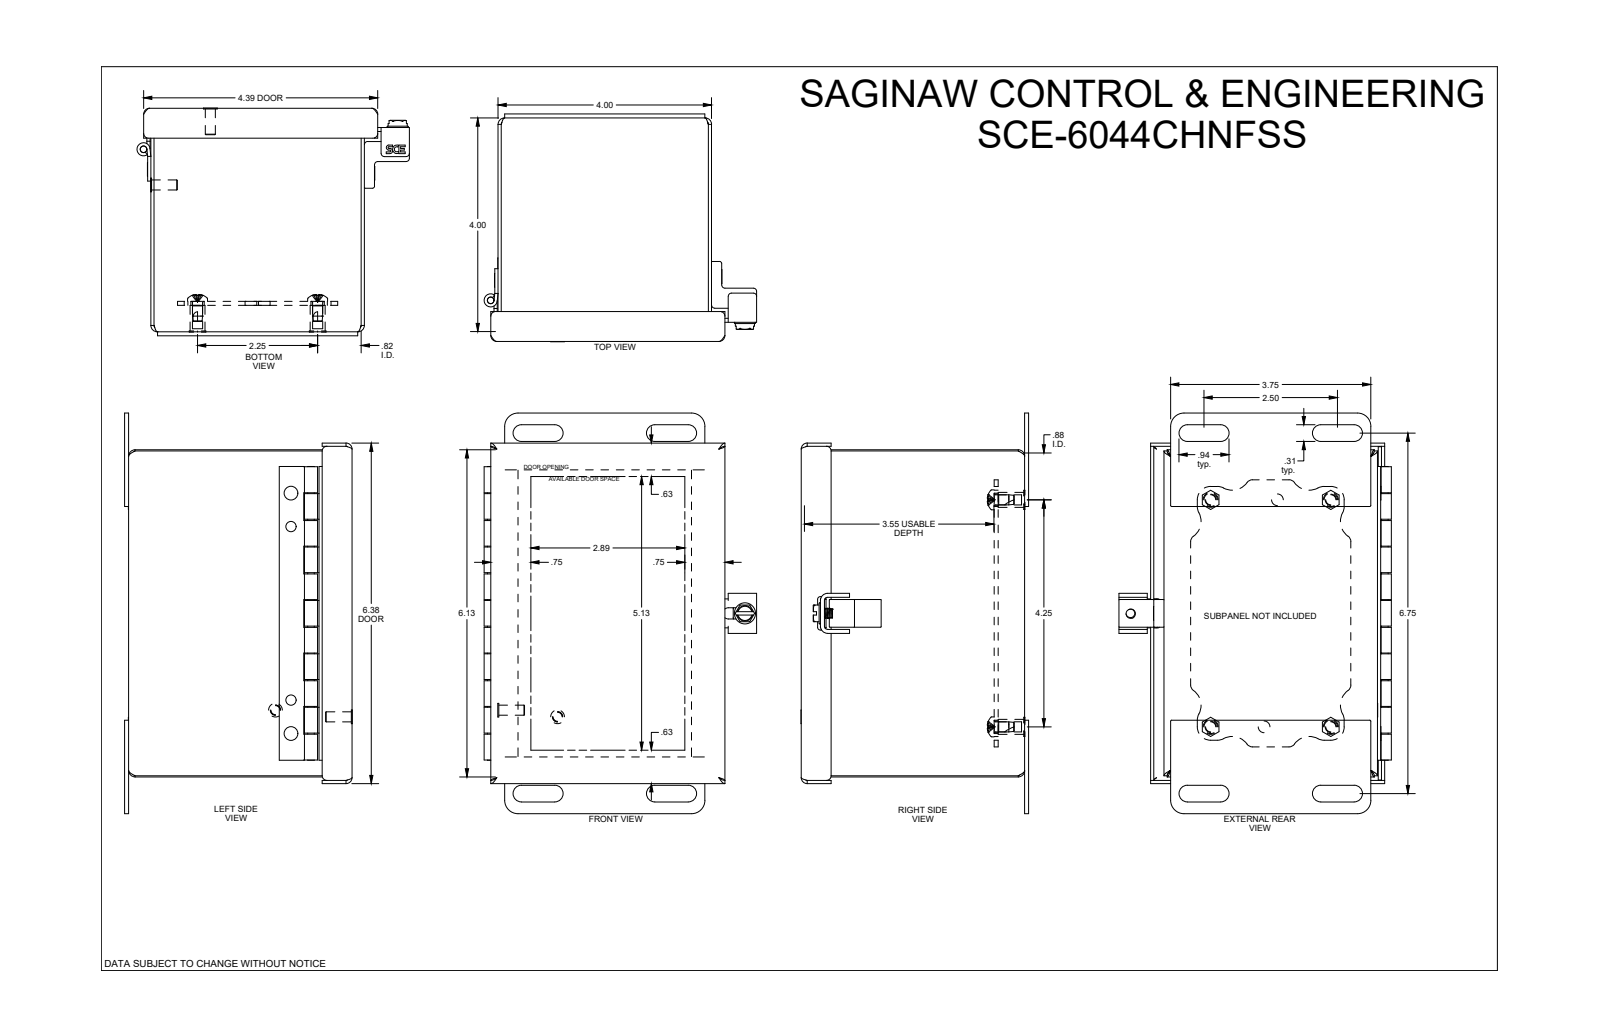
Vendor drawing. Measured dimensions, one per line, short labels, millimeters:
name: SCE-6044CHNFSS
written by: SolidWorks 2019 (CONFIG_CONTROL_DESIGN)
unit: mm
bodies: 0 solids, 1010 faces (467 planar, 275 cylindrical, 268 other)
size: 190.5 × 129.6 × 108.3
holes: 7× ⌀4.8, 5× ⌀4.9, 4× ⌀6.4, 4× ⌀7.1, 2× ⌀4.9, 2× ⌀5.5, 1× ⌀3.2, 1× ⌀4, 1× ⌀6.8
bosses: 10× ⌀4.8, 5× ⌀6.5, 4× ⌀9.5, 4× ⌀7.1, 1× ⌀10.1, 1× ⌀6.2, 1× ⌀3.1
rounds: 42× R0.3, 17× R1.5, 16× R6.4, 8× R0.2, 8× R1.3, 8× R2.8, 8× R3.2, 8× R4
face distances: 1.5, 100.1, 104.8, 1.5, 101.6, 154.1, 98.6, 106.3, 104.8, 103.3
hole spacings: 57.2, 57.2, 108, 109.5, 110.9, 122.1, 7.7, 8.8
